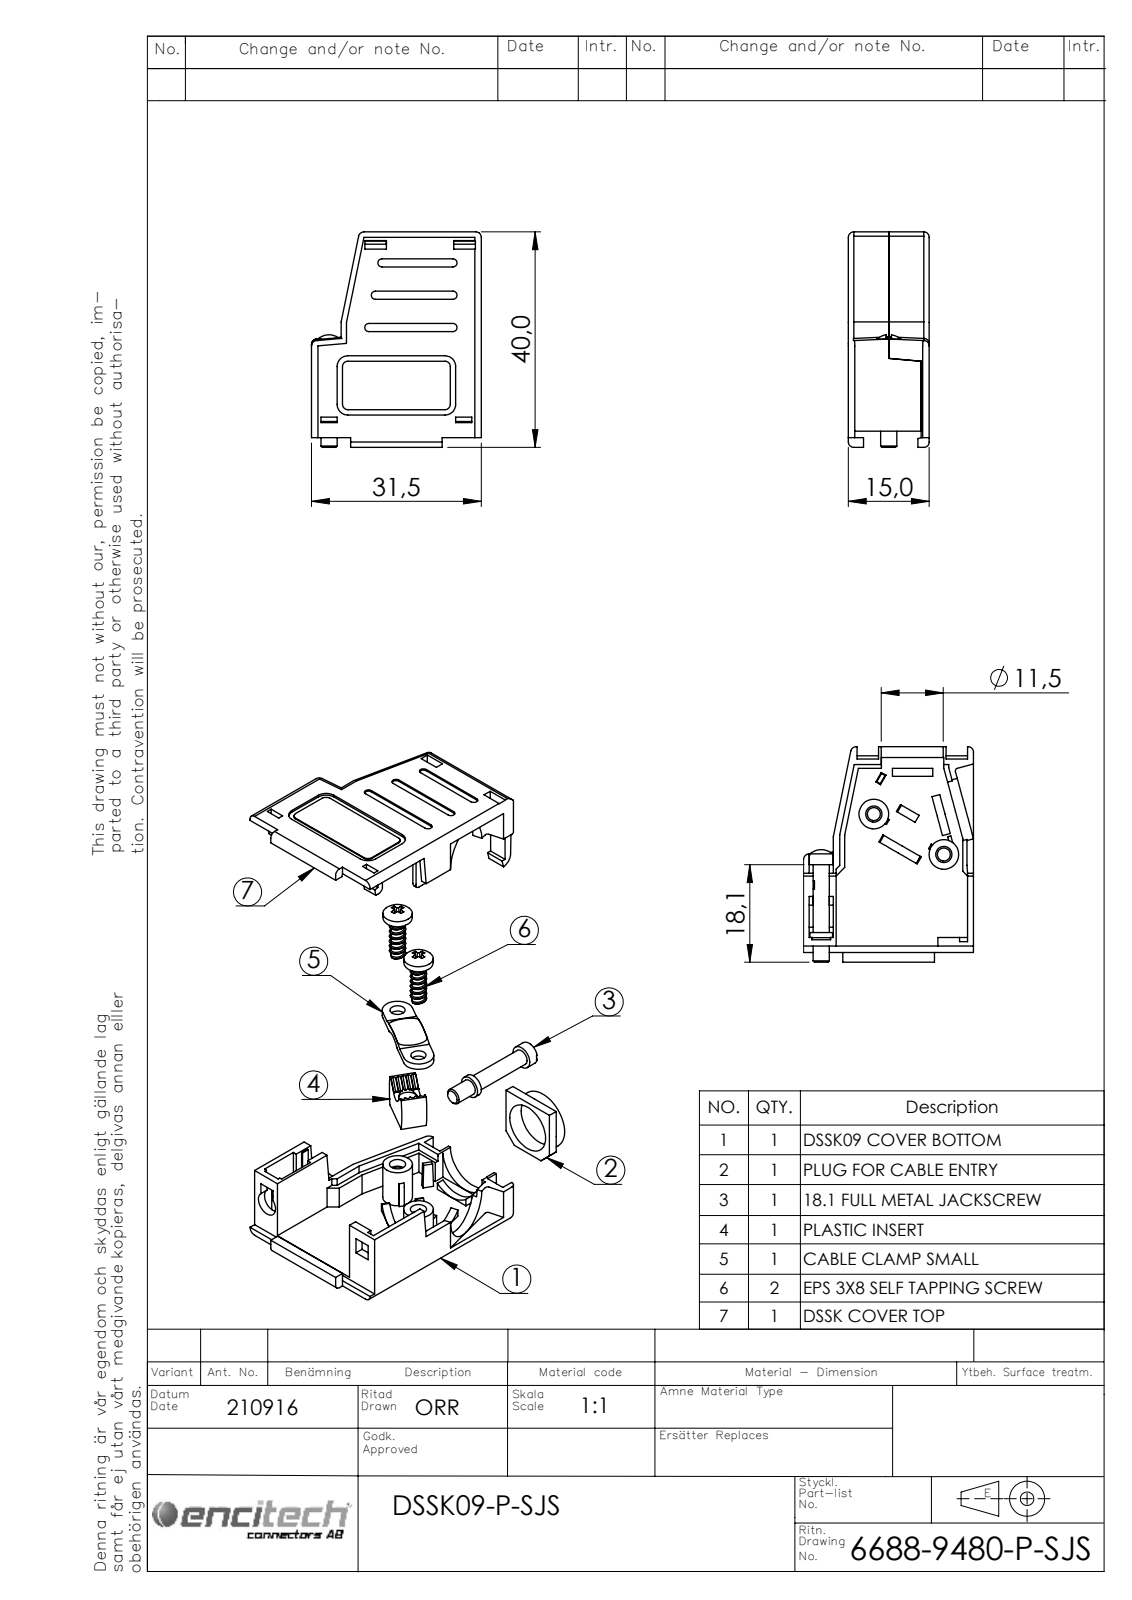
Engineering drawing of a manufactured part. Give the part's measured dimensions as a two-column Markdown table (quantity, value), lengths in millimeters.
| quantity | value |
| --- | --- |
| part name | 6855-0109-01; 6826-0133-01; 6688-9480-P-SJS; 6830-0106-01 (+4 more) |
| STEP written by | SolidWorks 2021 (AUTOMOTIVE_DESIGN) |
| units | millimeters |
| bodies | 10 solids, 650 faces (439 planar, 164 cylindrical, 47 other) |
| overall size | 40 × 31.5 × 15 |
| volume | 6 797 mm³ |
| surface area | 10 269 mm² |
| round holes (diameter × count) | 2.4 × 2, 2.8 × 2, 3 × 2, 3.5 × 1, 4.5 × 1, 9.4 × 1, 11.5 × 1, 11.6 × 1 |
| round bosses / shafts (diameter × count) | 5.5 × 2, 5.45 × 2, 2.46 × 2, 11.4 × 1, 4.4 × 1, 4.2 × 1, 3 × 1 |
| partial cylindrical surfaces (radius × count) | 1 × 20, 0.5 × 6, 0.75 × 6, 2 × 6, 1.2 × 4, 0.1 × 2, 2.85 × 2, 13 × 2 |
| main face-to-face distances | 13.3, 1.7, 1.5, 11.6, 15, 13.1, 1.3, 1.6, 1.2, 14.8 |
| hole center spacings | 7.45, 7.55, 15, 16.89 |
